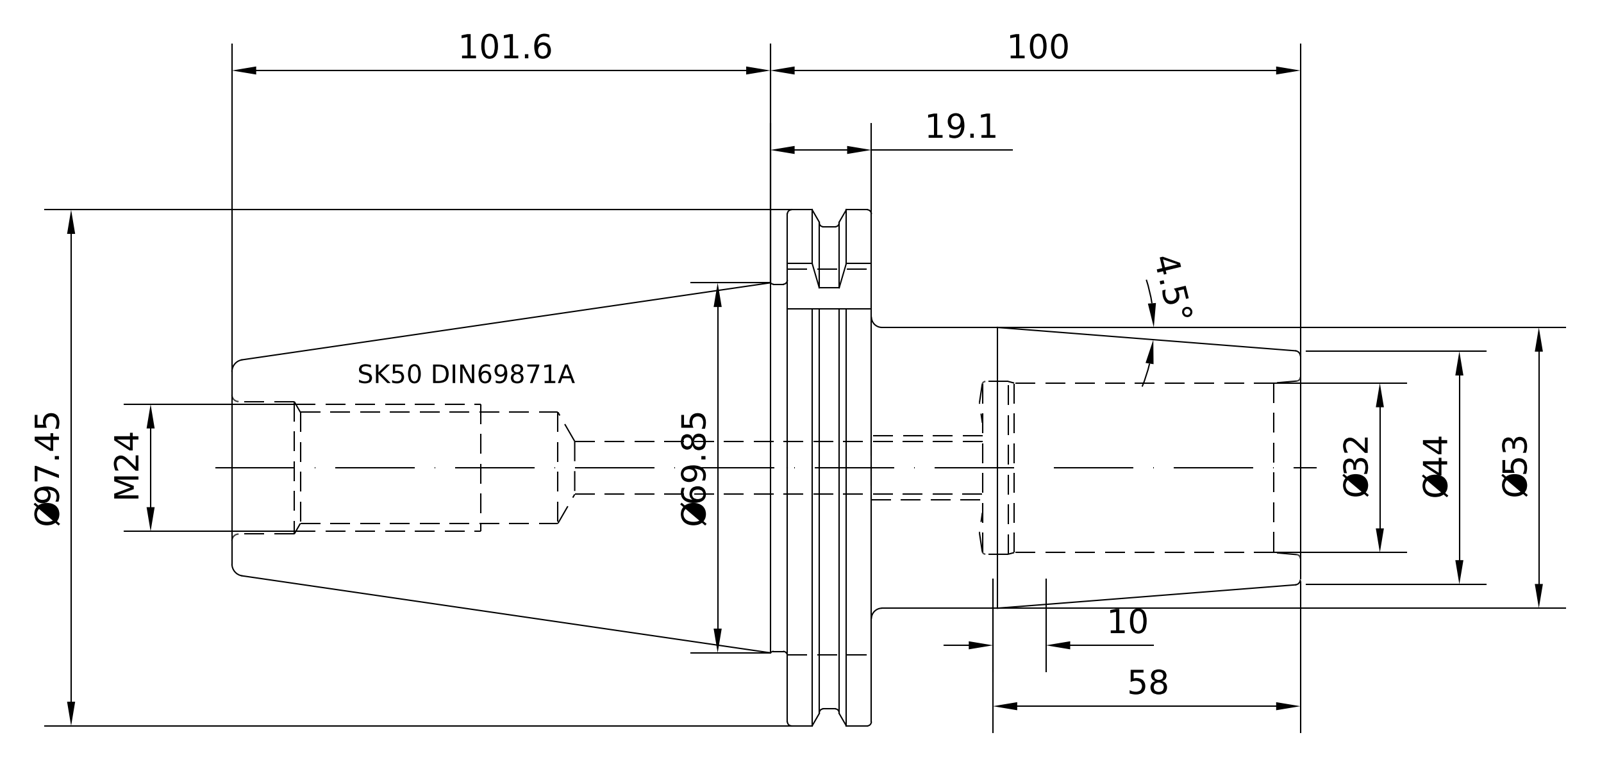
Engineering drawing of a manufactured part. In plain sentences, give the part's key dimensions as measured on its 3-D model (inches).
The part is named "50-440-32". Its 3-D file was written by "PRO/ENGINEER BY PARAMETRIC TECHNOLOGY CORPORATION, 2010430 (CONFIG_CONTROL_DESIGN)". It is 1 solid with 93 faces: 21 planar, 24 cylindrical and 48 other. Overall it measures 7.937 by 3.837 by 3.701 inches. Its volume is 27.39 cubic inches and its surface area 93.92 square inches. Round holes: 1 of diameter 0.817, 1 of diameter 0.985, 1 of diameter 1.012, 1 of diameter 1.26. Round bosses or shafts: 1 of diameter 3.583, 1 of diameter 2.722, 1 of diameter 2.087, 1 of diameter 0.945. Partial cylindrical surfaces (rounded edges, fillets, slot ends): 1 of radius 0.069, 1 of radius 1.919. The main face-to-face distances are 0.624, 1.409, 0.785, 3.811, 3.187, 2.402, 2.866, 4.126, 4.75, 5.535.
